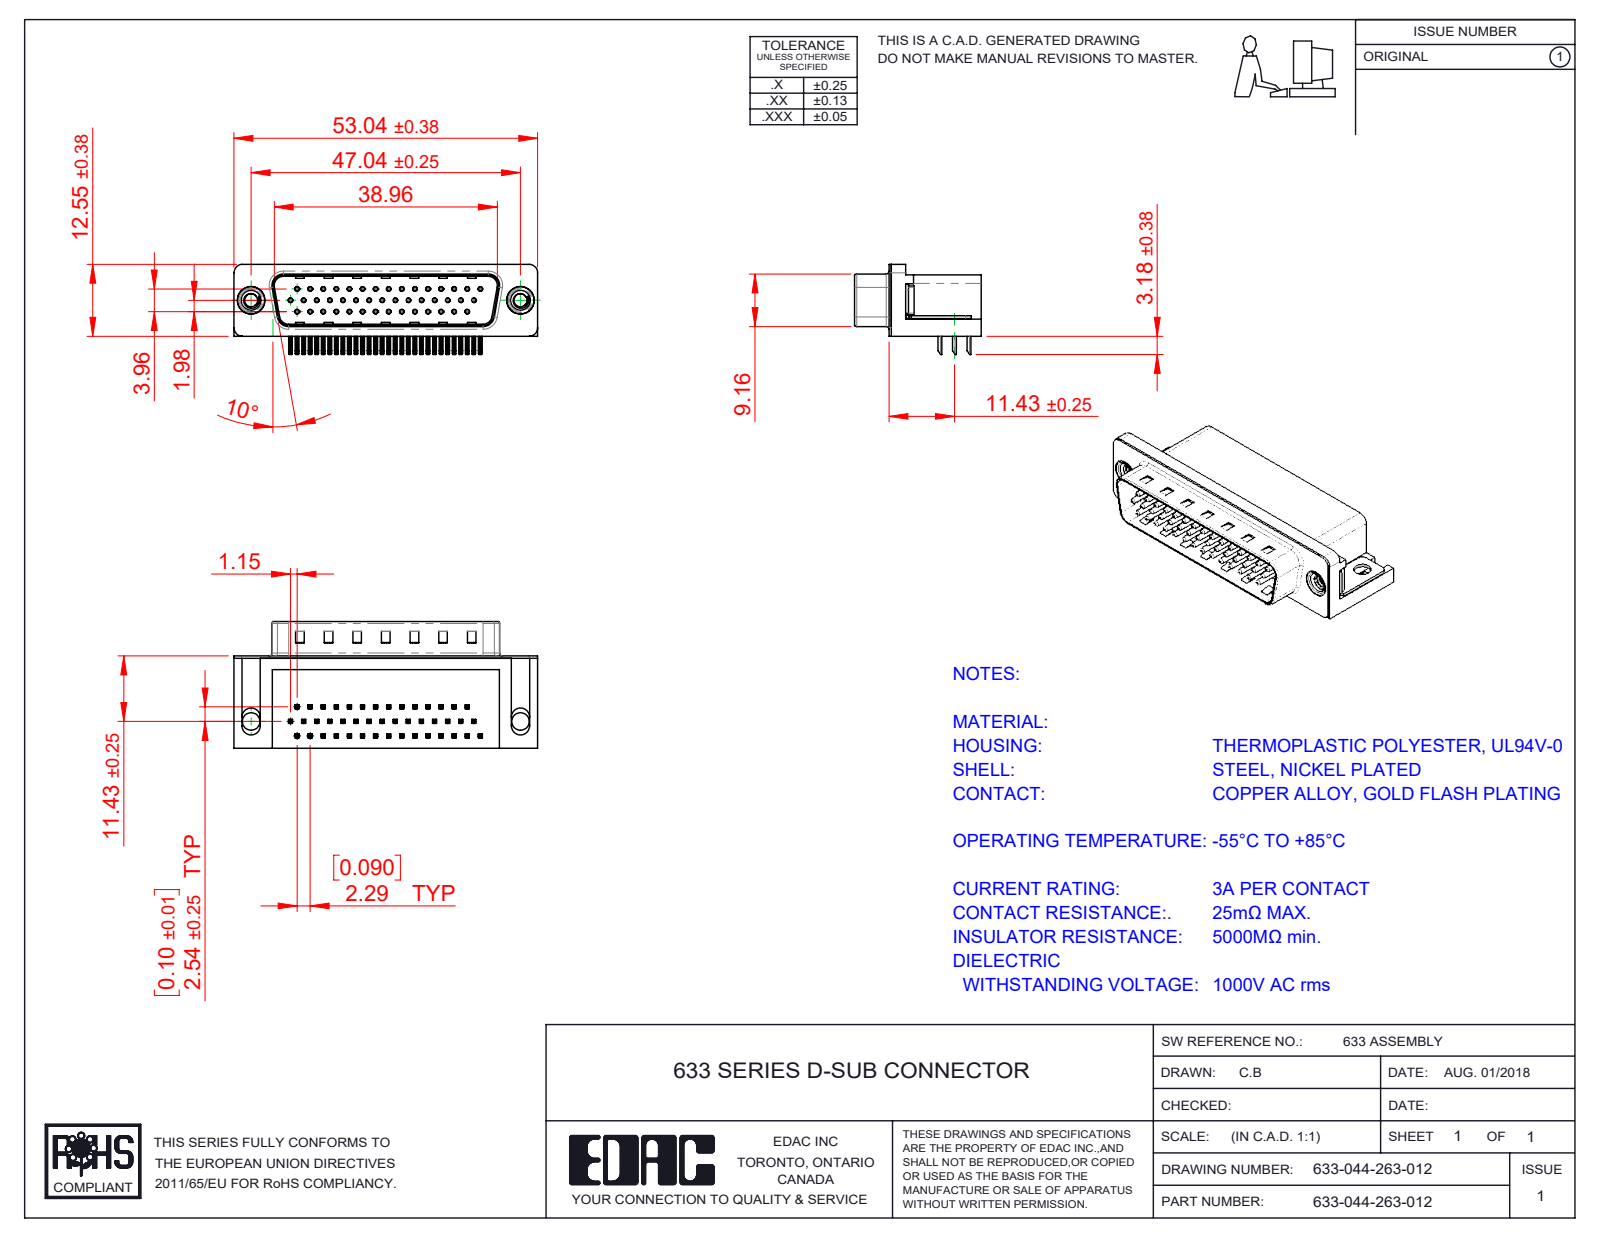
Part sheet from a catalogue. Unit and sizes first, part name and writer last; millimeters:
Units: millimetres
Overall size (bounding box): 53.04 × 22.1 × 15.73
Round holes (diameter × count): ⌀0.35 ×44, ⌀0.8 ×44, ⌀2.26 ×2, ⌀3.05 ×2, ⌀4 ×2, ⌀4.8 ×2, ⌀5 ×2
Round bosses / shafts (diameter × count): ⌀0.75 ×44, ⌀4.9 ×2, ⌀4.75 ×2, ⌀3.9 ×2
Partial cylindrical surfaces — rounded edges, fillets, slot ends (radius × count): R0.25 ×184, R0.12 ×88, R1 ×16, R0.5 ×9, R1.6 ×8, R1.5 ×7, R0.9 ×4, R2 ×4
Main face-to-face distances: 0.4, 10.35, 15.7, 2.9, 8.76, 2.5, 2.1, 16.1, 10.7, 2.54
Hole centre spacings: 2.29, 4.57, 4.58, 2.28, 6.87, 9.16, 11.45, 2.27
Volume: 8 114 mm³ · Surface area: 10 206 mm²
Bodies: 50 solids, 3688 faces (2315 planar, 1060 cylindrical, 313 other)
Part name (STEP PRODUCT): 633 Contact Middle; 633 Contact Bottom; 633 Shell_44 Contact; 633 Housing_44 Contact (+4 more)
STEP written by: SolidWorks 2016 (CONFIG_CONTROL_DESIGN)
